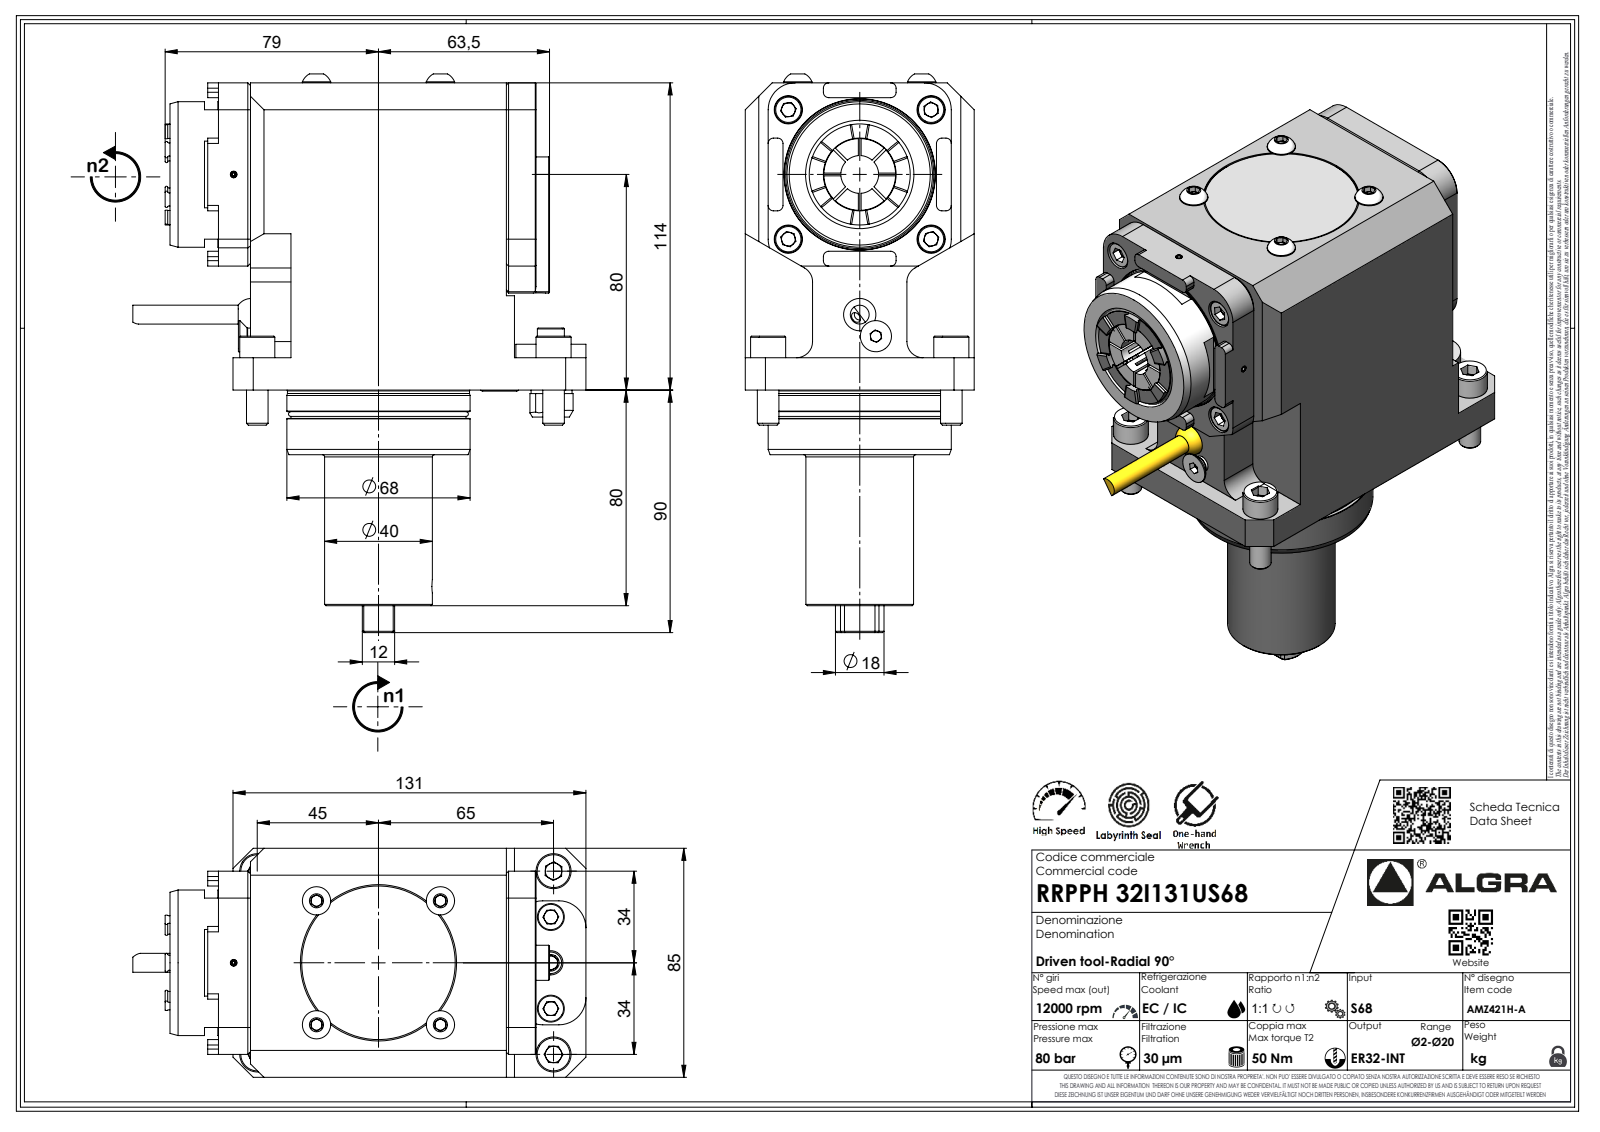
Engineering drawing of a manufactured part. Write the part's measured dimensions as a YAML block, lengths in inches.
part_name: "RRPPH32I131US68"
step_written_by: "SolidWorks 2023 (AUTOMOTIVE_DESIGN)"
units: inches
bodies: {solids: 9, faces: 834, planar: 420, cylindrical: 133, other: 281}
overall_size: [8.161, 6.622, 3.346]
volume: 80.61
surface_area: 179.3
round_holes:
  - {diameter: 0.083, count: 1}
  - {diameter: 0.157, count: 1}
  - {diameter: 1.063, count: 1}
  - {diameter: 1.317, count: 1}
round_bosses_or_shafts:
  - {diameter: 0.512, count: 5}
  - {diameter: 0.413, count: 4}
  - {diameter: 0.315, count: 4}
  - {diameter: 1.575, count: 2}
  - {diameter: 0.394, count: 2}
  - {diameter: 2.677, count: 1}
  - {diameter: 2.661, count: 1}
  - {diameter: 2.559, count: 1}
partial_cylinders:
  - {radius: 0.079, count: 17}
  - {radius: 0.394, count: 10}
  - {radius: 0.013, count: 7}
  - {radius: 0.02, count: 7}
  - {radius: 0.146, count: 7}
  - {radius: 0.236, count: 4}
  - {radius: 0.008, count: 1}
  - {radius: 0.354, count: 1}
face_to_face_distances: [3.346, 0.433, 4.488, 0.315, 3.15, 0.118, 0.335, 3.012, 1.417, 0.945]
